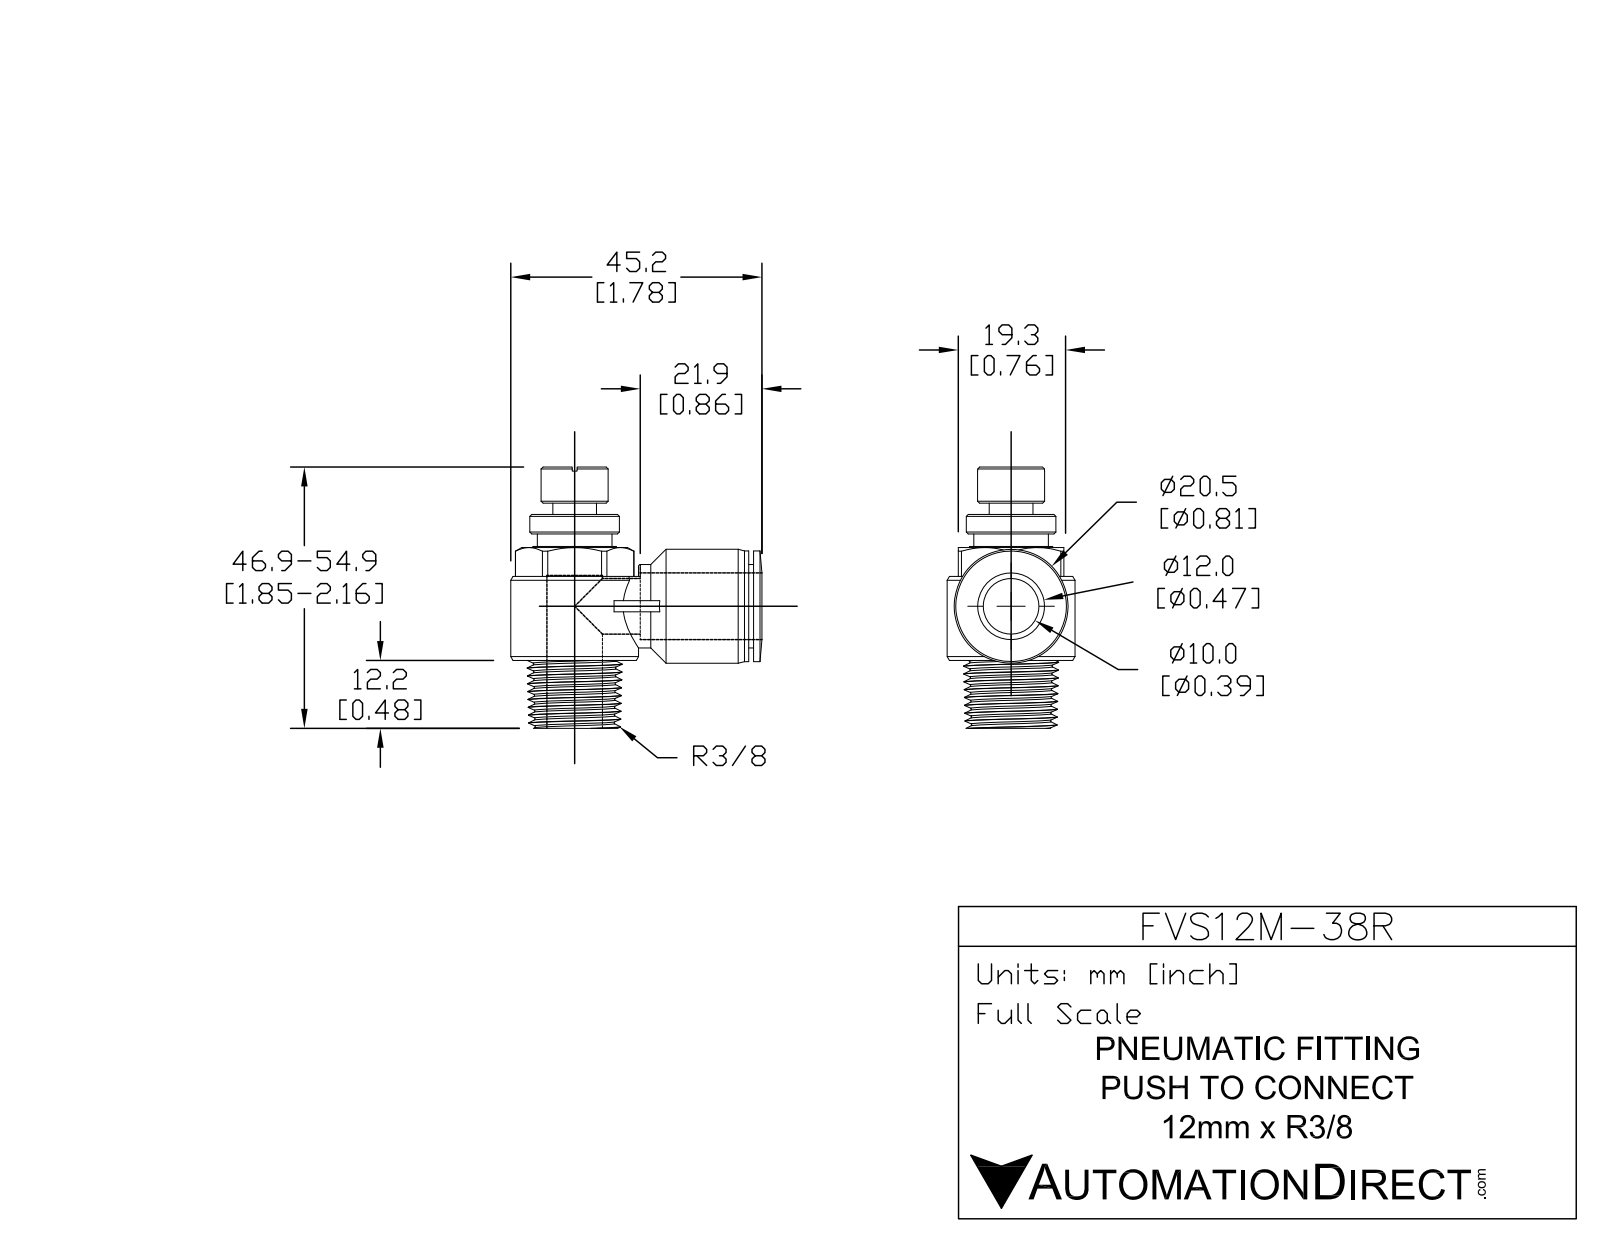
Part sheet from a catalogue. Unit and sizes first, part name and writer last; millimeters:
Units: millimetres
Overall size (bounding box): 56.8 × 45.2 × 23
Round holes (diameter × count): ⌀4.3 ×2, ⌀12.3 ×1
Round bosses / shafts (diameter × count): ⌀19 ×2, ⌀15 ×2, ⌀23 ×1, ⌀20.5 ×1, ⌀20 ×1, ⌀17.1 ×1, ⌀17.1 ×1, ⌀13.9 ×1
Partial cylindrical surfaces — rounded edges, fillets, slot ends (radius × count): R6 ×1, R8 ×1, R10.5 ×1
Main face-to-face distances: 1.2, 26.3, 19, 20.5, 5.8, 14.2, 34.7, 40.5, 18.3, 19.5
Volume: 16 580 mm³ · Surface area: 7 168 mm²
Bodies: 1 solid, 567 faces (255 planar, 144 cylindrical, 168 other)
Part name (STEP PRODUCT): FVS12M-38R
STEP written by: SolidWorks 2015 (AUTOMOTIVE_DESIGN)
